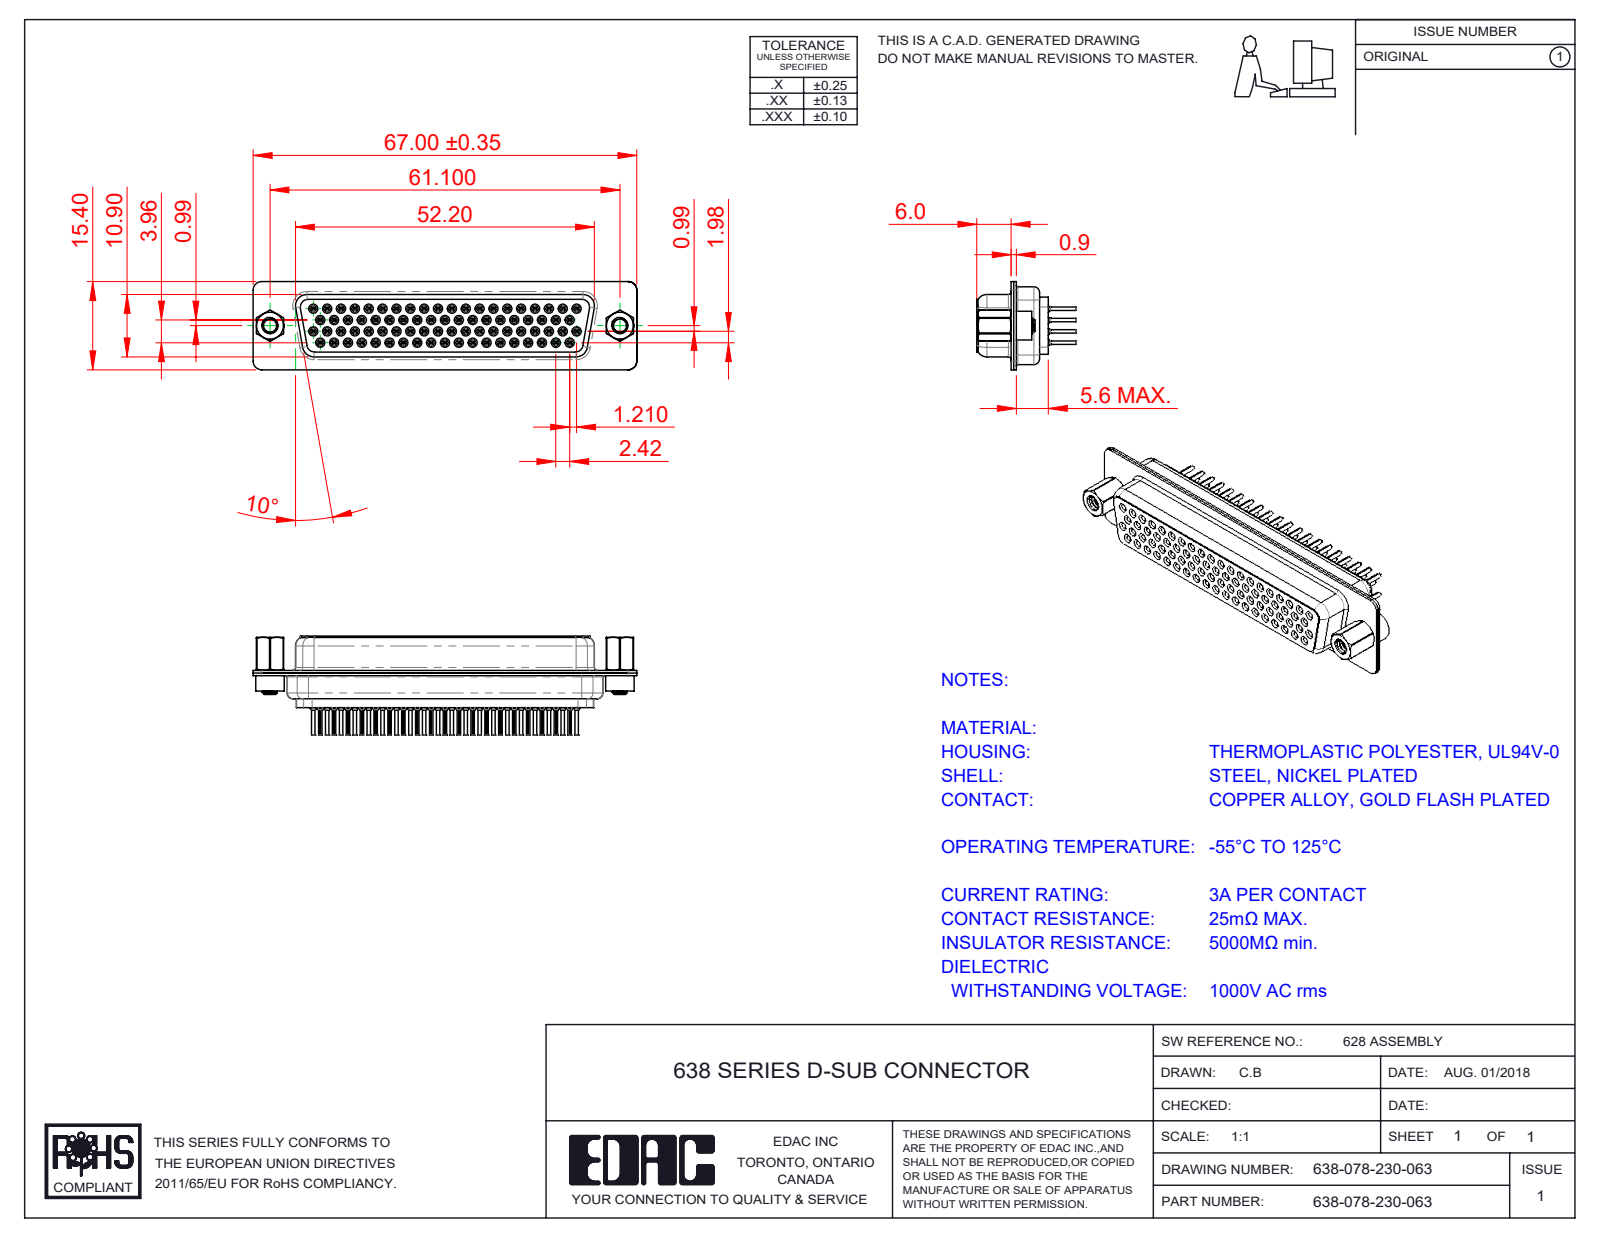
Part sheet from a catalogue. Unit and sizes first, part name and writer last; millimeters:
Units: millimetres
Overall size (bounding box): 67 × 17.3 × 15.4
Round holes (diameter × count): ⌀0.2 ×78, ⌀0.8 ×78, ⌀1 ×78, ⌀1.1 ×78, ⌀1.6 ×78, ⌀1.7 ×78, ⌀1.8 ×78, ⌀2.26 ×2, ⌀2.29 ×2, ⌀4 ×2, ⌀4.05 ×2, ⌀4.85 ×2
Round bosses / shafts (diameter × count): ⌀2 ×78, ⌀1.5 ×78, ⌀1.2 ×78, ⌀0.6 ×78, ⌀5 ×2, ⌀4.95 ×2, ⌀4.8 ×2, ⌀2.79 ×2
Partial cylindrical surfaces — rounded edges, fillets, slot ends (radius × count): R0.1 ×156, R0.28 ×39, R1.5 ×16, R2 ×12, R1.55 ×8, R0.25 ×4, R0.5 ×4, R0.55 ×4
Main face-to-face distances: 0.45, 0.4, 0.9, 1.35, 9.6, 11.8, 1.8, 11.4, 2.2, 13.15
Hole centre spacings: 2.42, 4.84, 7.26, 9.68, 6.06, 12.1, 6.96, 8.48
Volume: 6 088 mm³ · Surface area: 21 007 mm²
Bodies: 85 solids, 10311 faces (2507 planar, 2783 cylindrical, 5021 other)
Part name (STEP PRODUCT): 638 Housing_78 Contacts; 638 Shell Rear_78 Contacts; 638 Contact Row 2_30; 638 Shell Front_78 Contacts (+6 more)
STEP written by: SolidWorks 2020 (CONFIG_CONTROL_DESIGN)
